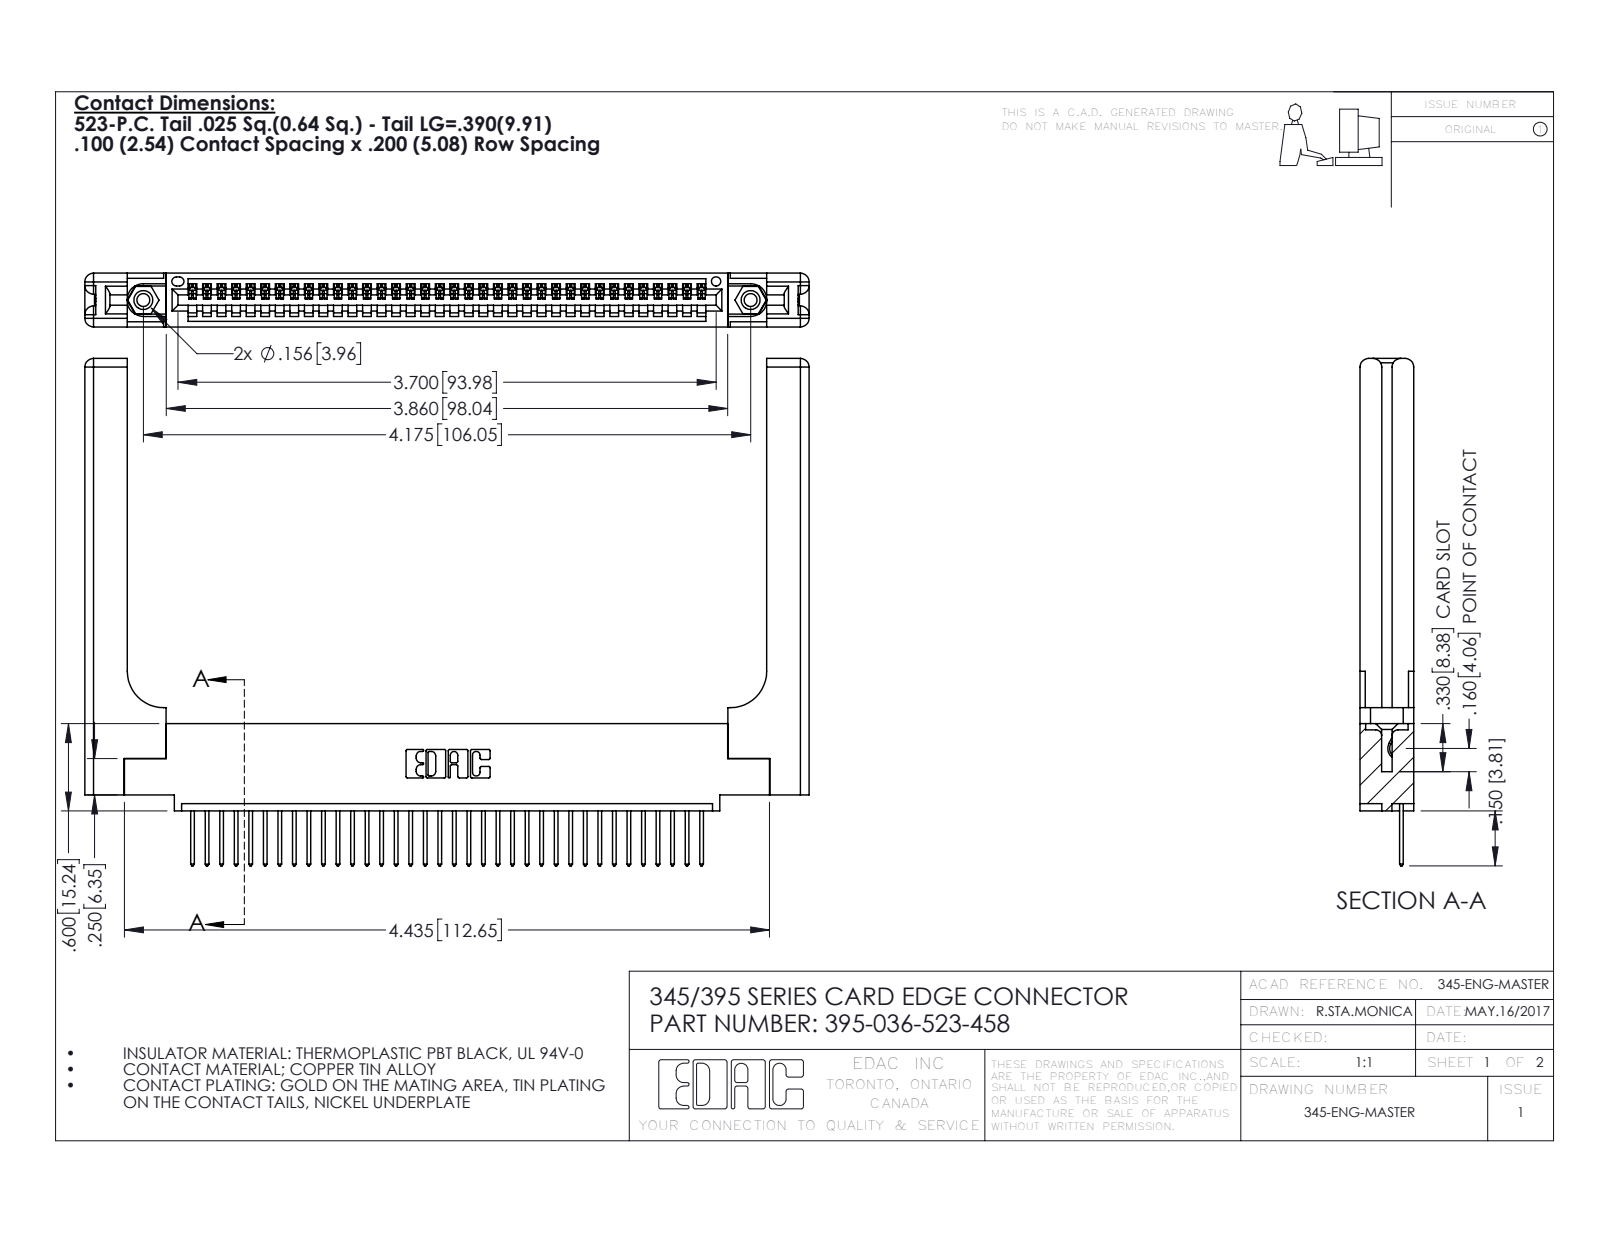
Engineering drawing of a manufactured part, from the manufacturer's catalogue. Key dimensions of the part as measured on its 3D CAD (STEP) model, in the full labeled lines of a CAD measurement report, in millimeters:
Part name (STEP PRODUCT): 345 Part_0.110 Offset - 0.156 Dia-TH; 395-036-523-458; 345-292-001_345-293-123; 345-220-058_345-220-058 (+1 more)
STEP written by: SolidWorks 2016 (CONFIG_CONTROL_DESIGN)
Units: millimetres
Bodies: 41 solids, 2474 faces (1672 planar, 742 cylindrical, 60 other)
Overall size (bounding box): 126.5 × 88.6 × 9.4
Volume: 20 390 mm³ · Surface area: 21 130 mm²
Round holes (diameter × count): ⌀2.3 ×2, ⌀3.2 ×2, ⌀4 ×2, ⌀1.6 ×1
Round bosses / shafts (diameter × count): ⌀3.9 ×2
Partial cylindrical surfaces — rounded edges, fillets, slot ends (radius × count): R0.2 ×72, R0.3 ×72, R0.3 ×22, R1.5 ×16, R0.2 ×6, R0.8 ×6, R0.7 ×3, R0.8 ×2
Main face-to-face distances: 9.4, 1.8, 7.6, 2.5, 6.9, 0.6, 5.1, 3.8, 3.8, 5.7
Hole centre spacings: 6.9, 100.1, 106
